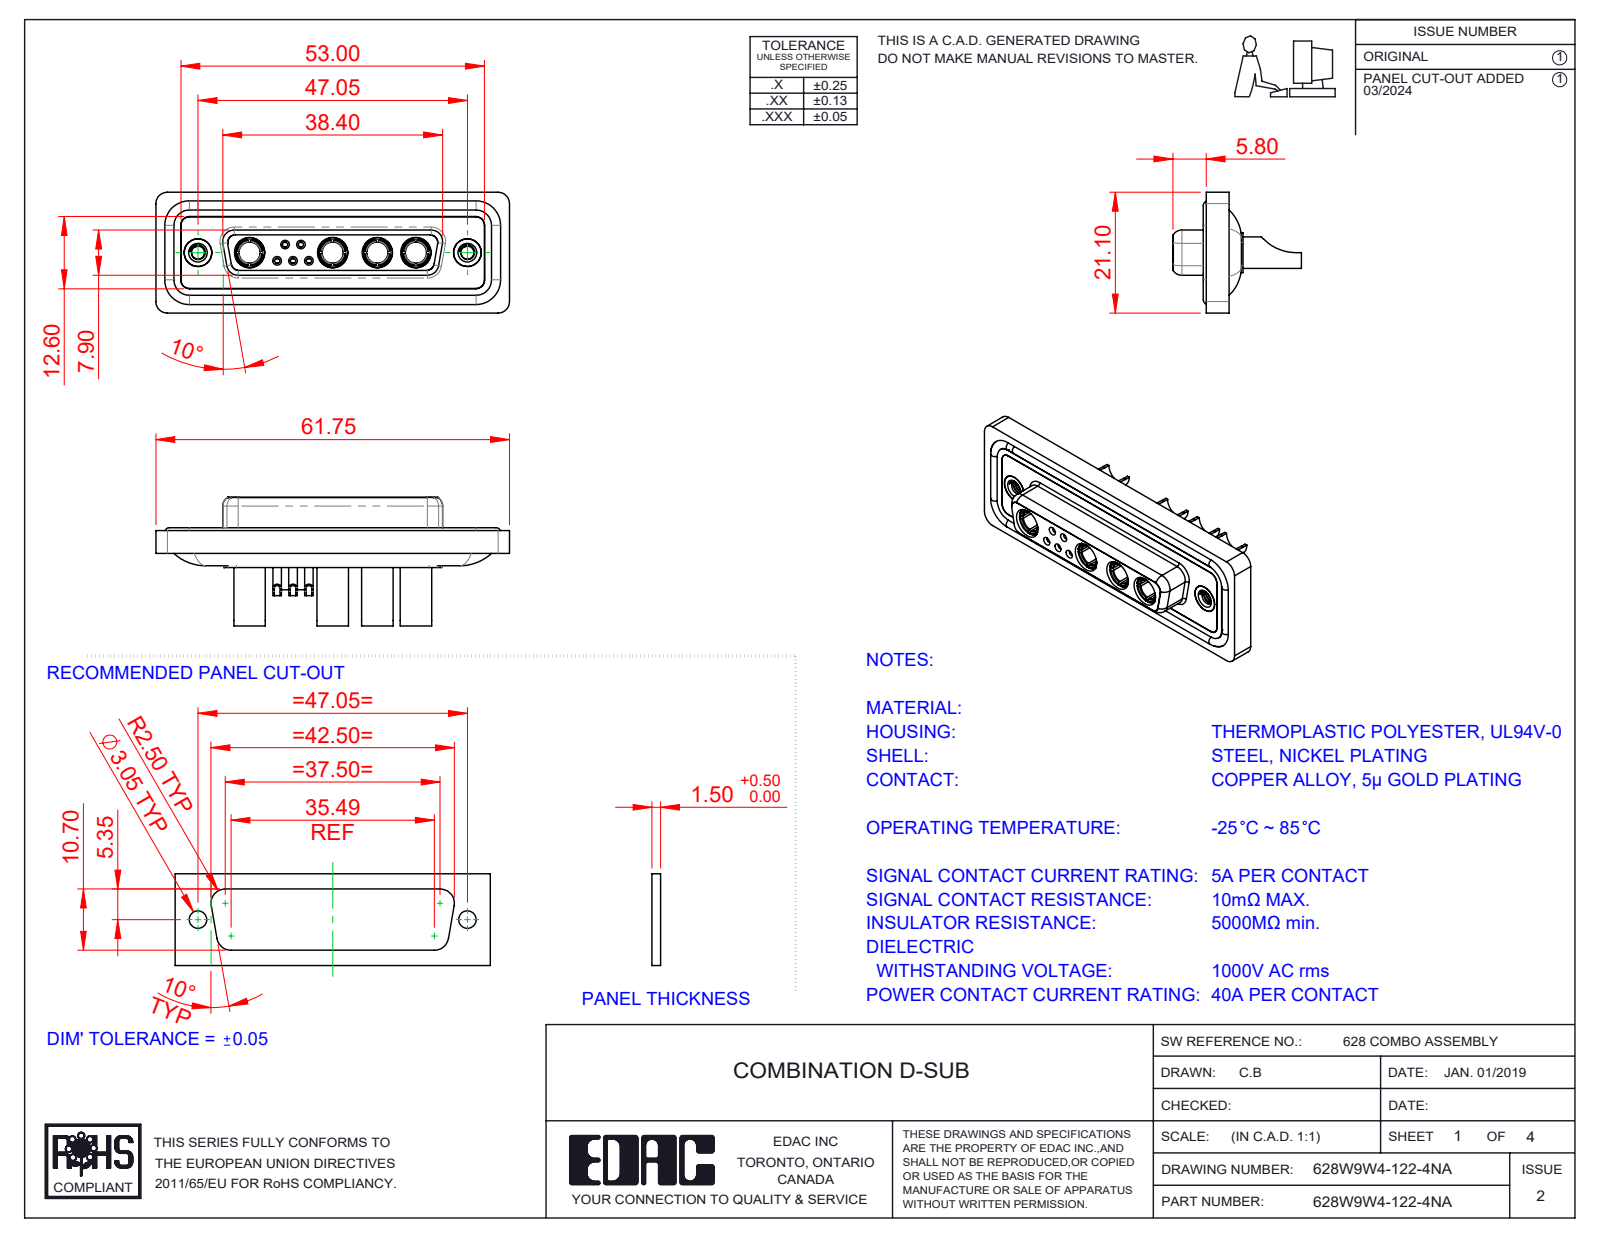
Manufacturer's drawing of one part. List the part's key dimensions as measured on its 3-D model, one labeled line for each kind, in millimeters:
Part name (STEP PRODUCT): 628W9W4-122-4NA; 628Combo Shell Rear_25 Contacts; 628Combo Shell Front_25 Contacts; 628Combo Housing_9W4 (+5 more)
STEP written by: SolidWorks 2023 (CONFIG_CONTROL_DESIGN)
Units: millimetres
Bodies: 20 solids, 967 faces (314 planar, 391 cylindrical, 262 other)
Overall size (bounding box): 61.75 × 22.45 × 21.1
Volume: 8 396 mm³ · Surface area: 14 174 mm²
Round holes (diameter × count): ⌀4.85 ×6, ⌀0.9 ×5, ⌀1 ×5, ⌀1.1 ×5, ⌀1.5 ×5, ⌀2 ×5, ⌀3.7 ×4, ⌀4.6 ×4, ⌀5.3 ×4, ⌀1.6 ×3, ⌀1.7 ×2, ⌀2.26 ×2
Round bosses / shafts (diameter × count): ⌀1.6 ×6, ⌀2.2 ×5, ⌀5.5 ×4, ⌀5.2 ×4, ⌀4.96 ×4, ⌀4.75 ×4, ⌀3.75 ×4, ⌀4.95 ×2
Partial cylindrical surfaces — rounded edges, fillets, slot ends (radius × count): R1.5 ×22, R2 ×18, R1.35 ×8, R1.6 ×8, R1 ×6, R0.25 ×4, R0.5 ×4, R0.6 ×4
Main face-to-face distances: 0.4, 7.45, 1.8, 5.65, 0.5, 7.05, 6.6, 1.6, 1.1, 2.9
Hole centre spacings: 3.16, 2.77, 5.03, 2.76, 4.4, 5.02, 5.54, 5.73
